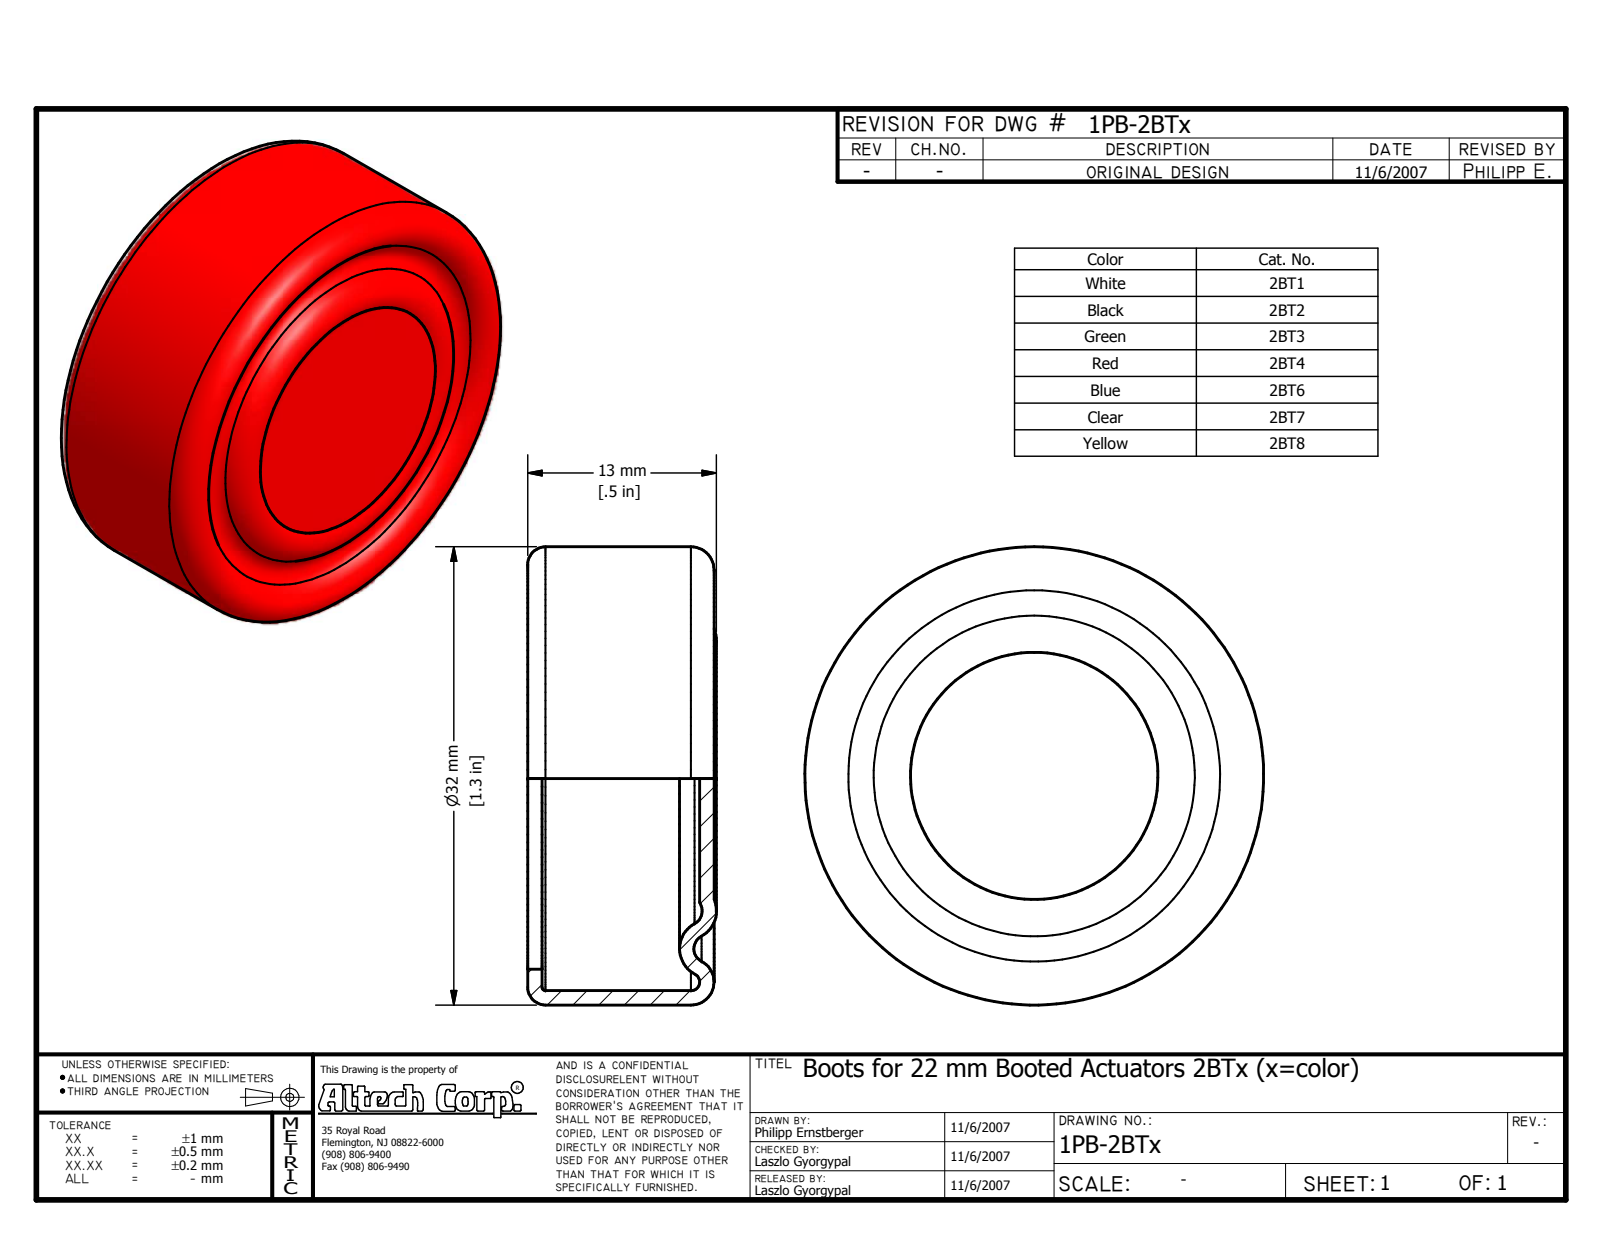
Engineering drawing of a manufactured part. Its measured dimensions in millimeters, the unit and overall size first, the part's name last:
Units: millimetres
Overall size (bounding box): 32 × 32 × 13.17
Round holes (diameter × count): ⌀27 ×1, ⌀30 ×1
Round bosses / shafts (diameter × count): ⌀32 ×1
Main face-to-face distances: 1, 12, 13, 11
Volume: 2 114 mm³ · Surface area: 4 317 mm²
Bodies: 1 solid, 16 faces (4 planar, 3 cylindrical, 9 other)
Part name (STEP PRODUCT): 2BT4_new_version
STEP written by: Autodesk Inventor 2008 (AUTOMOTIVE_DESIGN)
